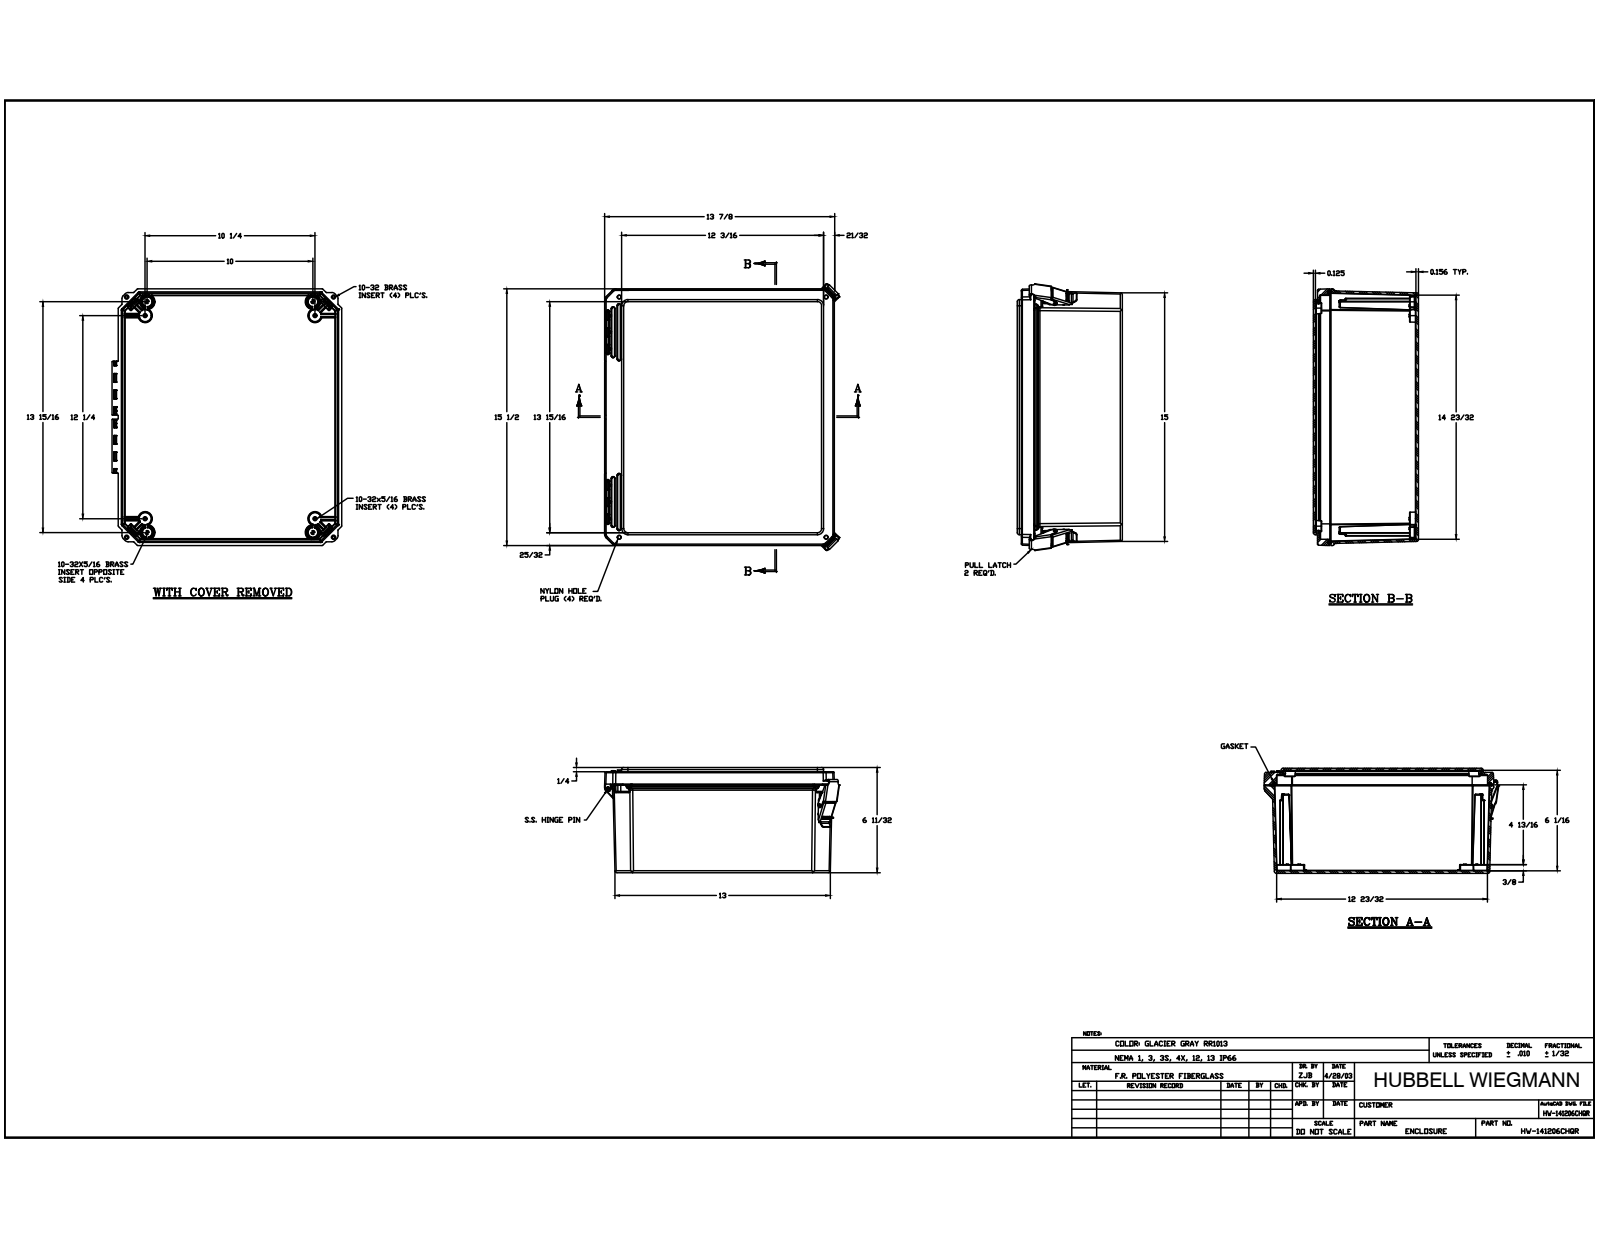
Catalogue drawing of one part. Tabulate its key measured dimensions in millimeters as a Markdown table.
| quantity | value |
| --- | --- |
| part name | DS141206BOX; BRASS INSERT-(; BRASS INSERT-(_1; BRASS INSERT-(_2 (+6 more) |
| STEP written by | Autodesk Inventor 2014 (AUTOMOTIVE_DESIGN) |
| units | millimeters |
| bodies | 35 solids, 2607 faces (889 planar, 1050 cylindrical, 668 other) |
| overall size | 409.71 × 360.39 × 161.07 |
| volume | 2 000 000 mm³ |
| surface area | 1 060 000 mm² |
| round holes (diameter × count) | 3.96 × 16, 3.43 × 9, 3.86 × 8, 3.81 × 4, 6.4 × 4, 6.43 × 4, 3.43 × 2, 5.56 × 2, 5.77 × 2, 7.94 × 2, 9.52 × 2, 3.48 × 1 |
| round bosses / shafts (diameter × count) | 6.25 × 16, 22.1 × 4, 7.62 × 4, 5.3 × 4, 11.05 × 2, 3.43 × 1 |
| partial cylindrical surfaces (radius × count) | 0.25 × 213, 0.51 × 111, 0.13 × 88, 0.76 × 61, 1.52 × 34, 1.59 × 27, 2.29 × 26, 0.76 × 24 |
| main face-to-face distances | 3.96, 3.17, 157.11, 161.07, 157.9, 153.94, 3.55, 3.53, 6.35, 150.76 |
| hole center spacings | 6.36, 40.18, 351.42, 272.08, 283.21, 340.76, 445.77, 460.06 |
